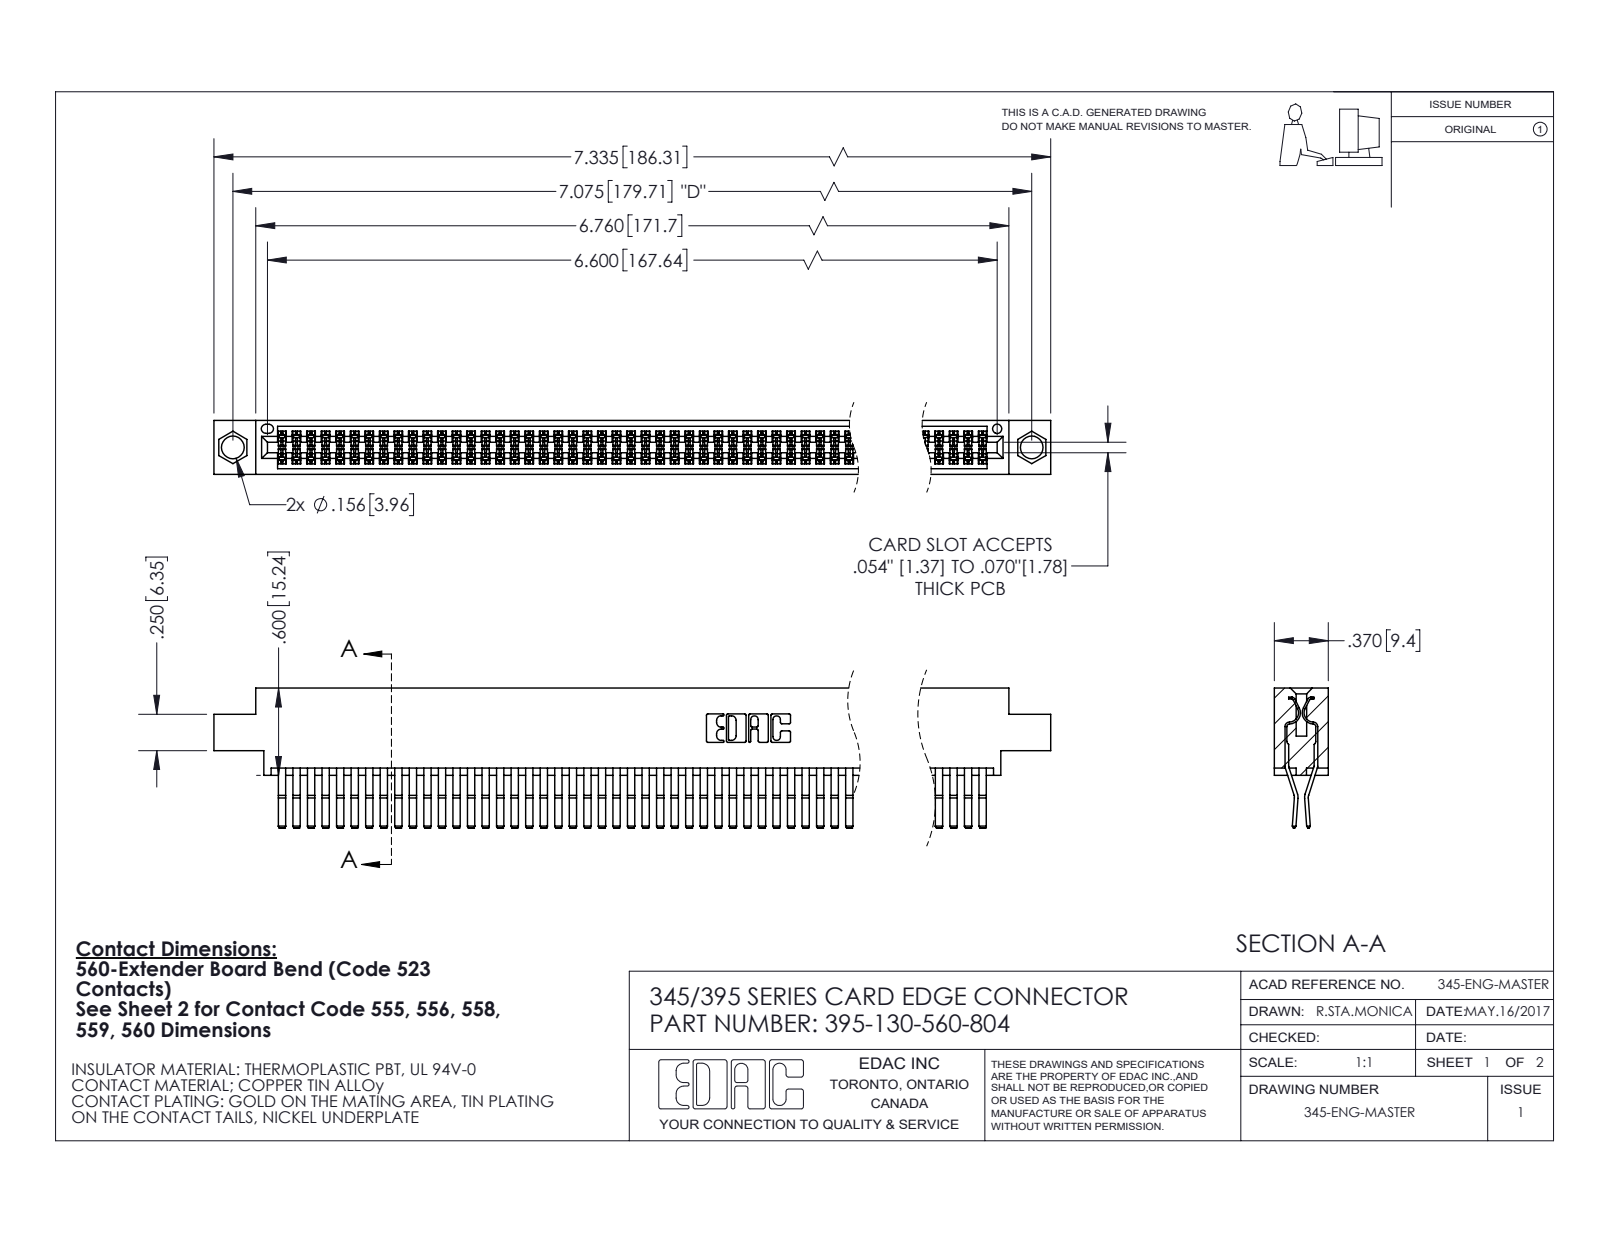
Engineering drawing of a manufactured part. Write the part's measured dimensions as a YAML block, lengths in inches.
part_name: "345-292-001_560 Tail; 345 Part_0.170 Offset - 0.156 Dia-TI; 395-130-560-804"
step_written_by: "SolidWorks 2020 (CONFIG_CONTROL_DESIGN)"
units: inches
bodies: {solids: 131, faces: 6904, planar: 4388, cylindrical: 2516, other: 0}
overall_size: [7.335, 0.962, 0.37]
volume: 1.156
surface_area: 47.48
round_holes:
  - {diameter: 0.156, count: 2}
  - {diameter: 0.064, count: 1}
partial_cylinders:
  - {radius: 0.006, count: 260}
  - {radius: 0.01, count: 22}
  - {radius: 0.007, count: 6}
  - {radius: 0.031, count: 6}
  - {radius: 0.026, count: 3}
  - {radius: 0.01, count: 2}
  - {radius: 0.014, count: 2}
  - {radius: 0.019, count: 2}
face_to_face_distances: [0.025, 0.072, 0.298, 0.37, 0.2, 0.098, 0.272, 0.225, 0.175, 0.149]
hole_center_spacings: [0.27, 6.839, 7.075]
